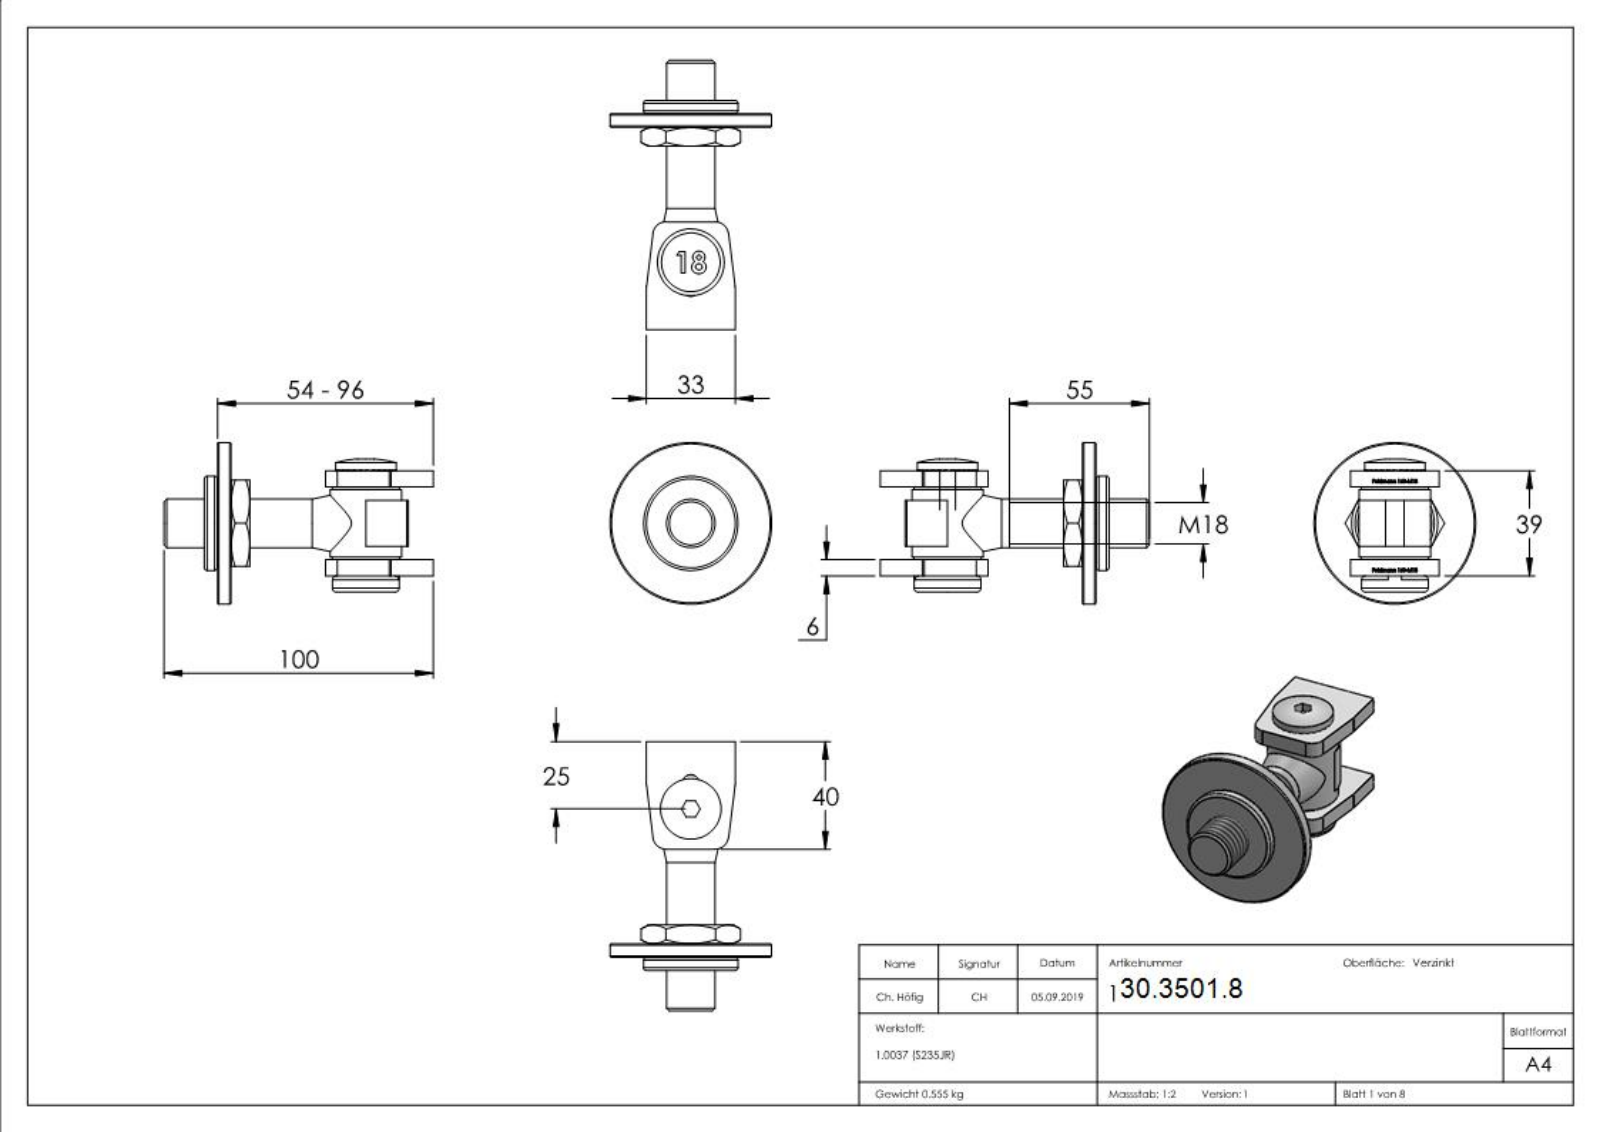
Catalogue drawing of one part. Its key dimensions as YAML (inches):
part_name: "160-M18 Teil5_160-M18 Teil5; 160-M18 Teil2_160-M18 Teil2; 160-M18 Teil4_160-M18 Teil4; 160-M18 Teil6_160-M18 Teil6 (+3 more)"
step_written_by: "SolidWorks 2015 (CONFIG_CONTROL_DESIGN)"
units: inches
bodies: {solids: 8, faces: 653, planar: 371, cylindrical: 58, other: 224}
overall_size: [3.937, 2.362, 2.362]
volume: 4.371
surface_area: 47.26
round_holes:
  - {diameter: 0.268, count: 1}
  - {diameter: 0.354, count: 1}
  - {diameter: 0.587, count: 1}
  - {diameter: 0.591, count: 1}
  - {diameter: 0.61, count: 1}
  - {diameter: 0.63, count: 1}
  - {diameter: 1.157, count: 1}
round_bosses_or_shafts:
  - {diameter: 0.984, count: 2}
  - {diameter: 2.362, count: 1}
  - {diameter: 1.378, count: 1}
  - {diameter: 1.079, count: 1}
  - {diameter: 1.043, count: 1}
  - {diameter: 0.976, count: 1}
  - {diameter: 0.886, count: 1}
  - {diameter: 0.709, count: 1}
partial_cylinders:
  - {radius: 0.197, count: 4}
  - {radius: 0.591, count: 2}
  - {radius: 0.122, count: 1}
  - {radius: 0.394, count: 1}
face_to_face_distances: [0.236, 0.197, 1.299, 0.276, 1.26, 1.535, 0.039, 1.024, 1.063, 0.984]
